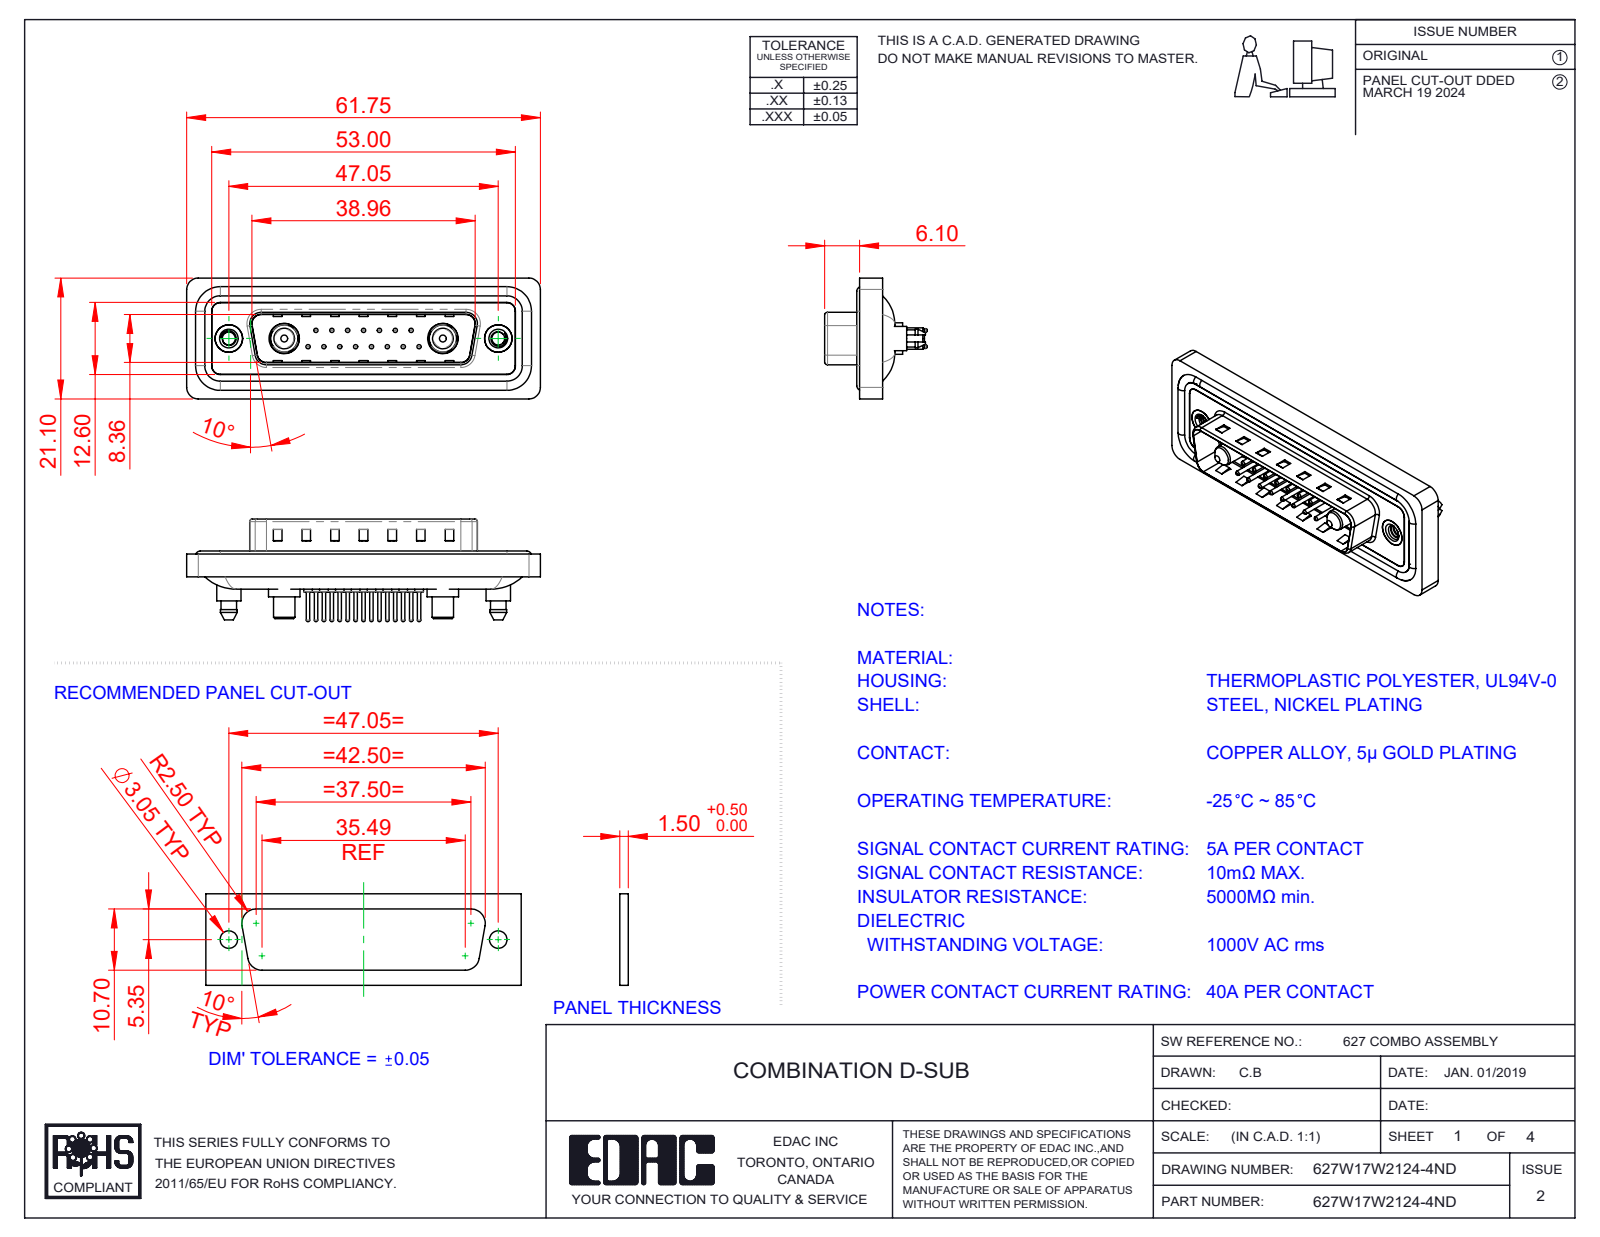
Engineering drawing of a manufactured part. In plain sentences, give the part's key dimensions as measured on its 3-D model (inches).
The part is named "627Combo Waterproof Housing_25 Contacts; 627Combo Contact Row 2_24; 627Combo Threaded Boardlock_D; 627W17W2124-4ND (+6 more)". Its 3-D file was written by "SolidWorks 2023 (CONFIG_CONTROL_DESIGN)". It is 26 solids with 1174 faces: 350 planar, 476 cylindrical and 348 other. Overall it measures 2.431 by 0.831 by 0.705 inches. Its volume is 0.454 cubic inches and its surface area 19.02 square inches. Round holes: 15 of diameter 0.03, 15 of diameter 0.063, 15 of diameter 0.079, 2 of diameter 0.089, 2 of diameter 0.157, 2 of diameter 0.189, 2 of diameter 0.191, 2 of diameter 0.197, 2 of diameter 0.209. Round bosses or shafts: 15 of diameter 0.059, 15 of diameter 0.024, 4 of diameter 0.063, 2 of diameter 0.217, 2 of diameter 0.213, 2 of diameter 0.205, 2 of diameter 0.193, 2 of diameter 0.187. Partial cylindrical surfaces (rounded edges, fillets, slot ends): 24 of radius 0.059, 18 of radius 0.079, 10 of radius 0.063, 8 of radius 0.02, 4 of radius 0.01, 4 of radius 0.024, 4 of radius 0.026, 4 of radius 0.035. The main face-to-face distances are 0.016, 0.059, 0.043, 0.063, 0.02, 0.122, 0.114, 0.032, 0.377, 0.161. The hole center spacings are 0.124, 0.109, 0.218, 0.327, 0.198, 0.295, 0.436, 0.198.
